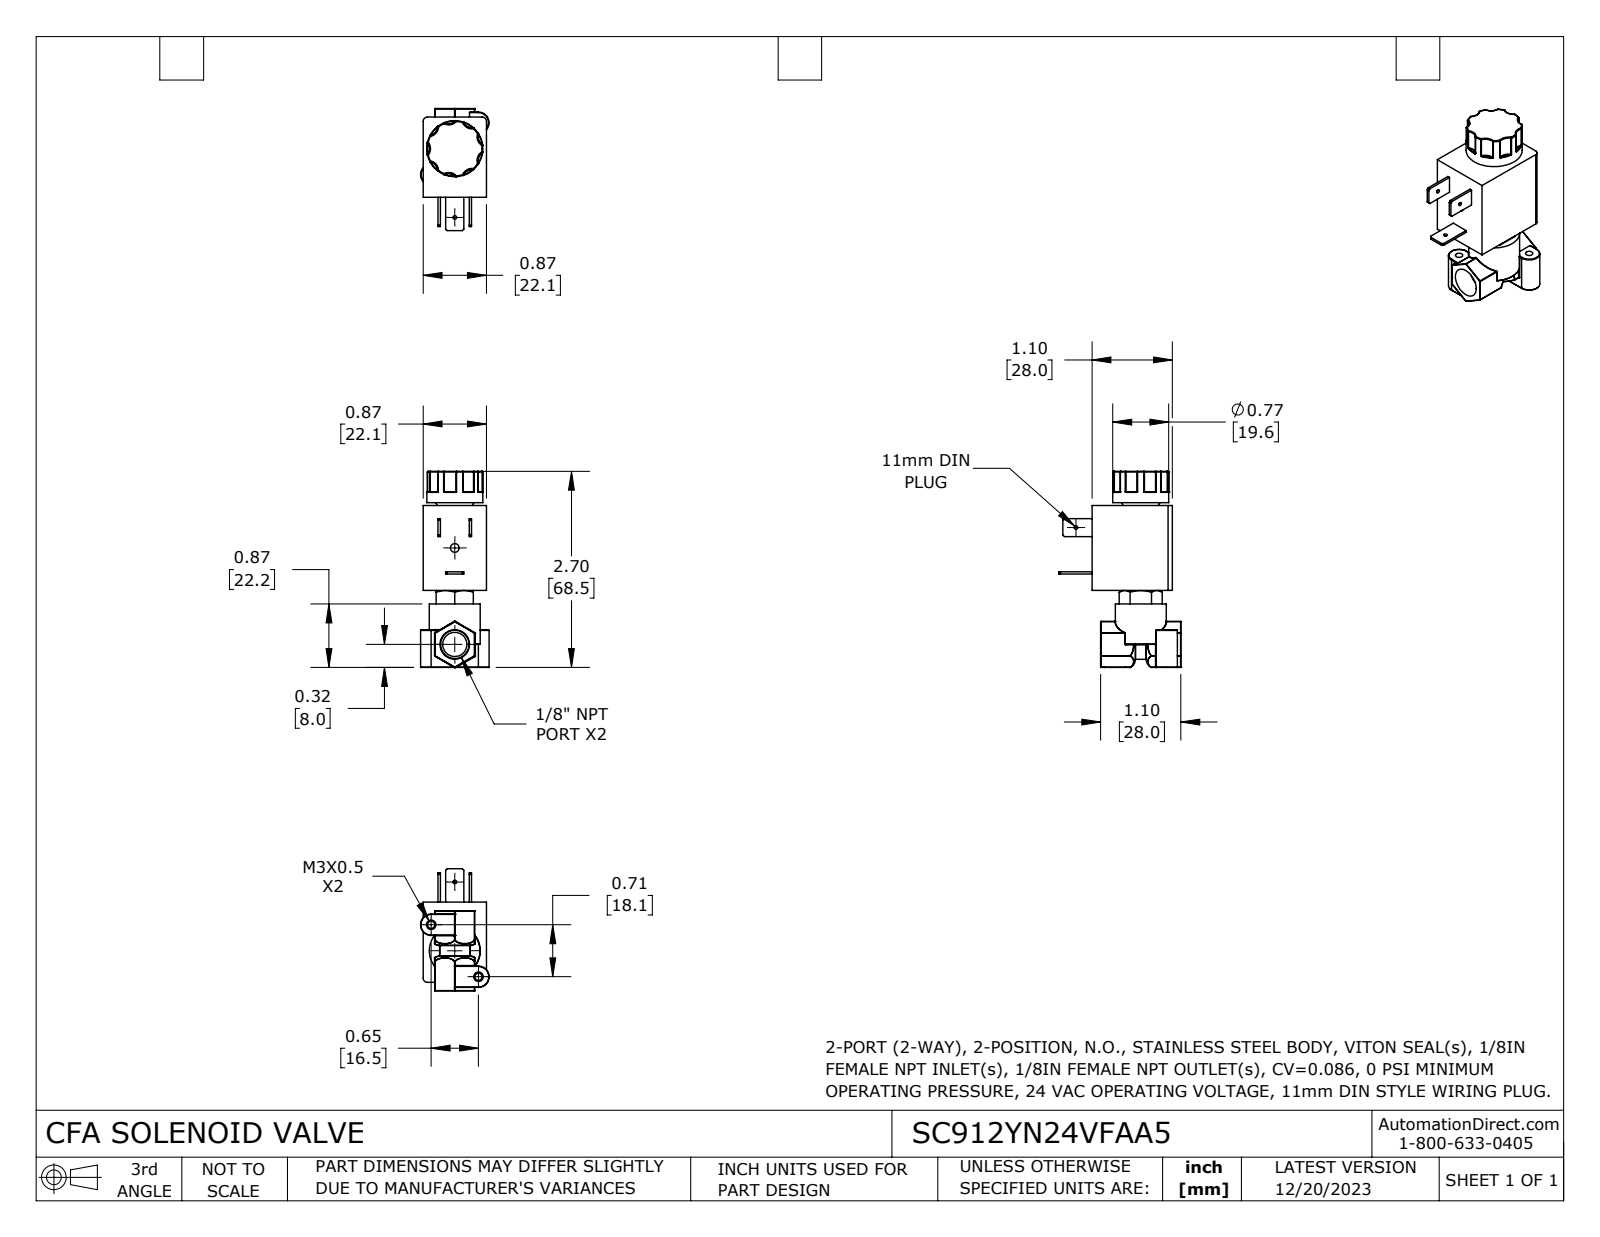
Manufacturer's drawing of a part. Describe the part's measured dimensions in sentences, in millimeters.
The part is named "SC912YN24VFAA5". Its 3-D file was written by "SolidWorks 2023 (CONFIG_CONTROL_DESIGN)". It is 1 solid with 397 faces: 76 planar, 110 cylindrical and 211 other. Overall it measures 68.5 by 42.6 by 23.9 millimeters. Its volume is 28 500 cubic millimeters and its surface area 9 064 square millimeters. Round holes: 2 of diameter 1.3, 2 of diameter 2.5, 1 of diameter 3, 1 of diameter 8.4. Round bosses or shafts: 1 of diameter 19.6, 1 of diameter 17.8. Partial cylindrical surfaces (rounded edges, fillets, slot ends): 29 of radius 0.1, 18 of radius 0.3, 12 of radius 0.2, 7 of radius 3.4, 2 of radius 0.4, 2 of radius 1.5, 2 of radius 3.4, 2 of radius 3.7. The main face-to-face distances are 22.1, 28, 29.6, 41.6, 11.9, 13.9, 0.8, 4.1, 18, 30.7. The hole center spacings are 17.1, 24.5, 33.7, 34.1.
